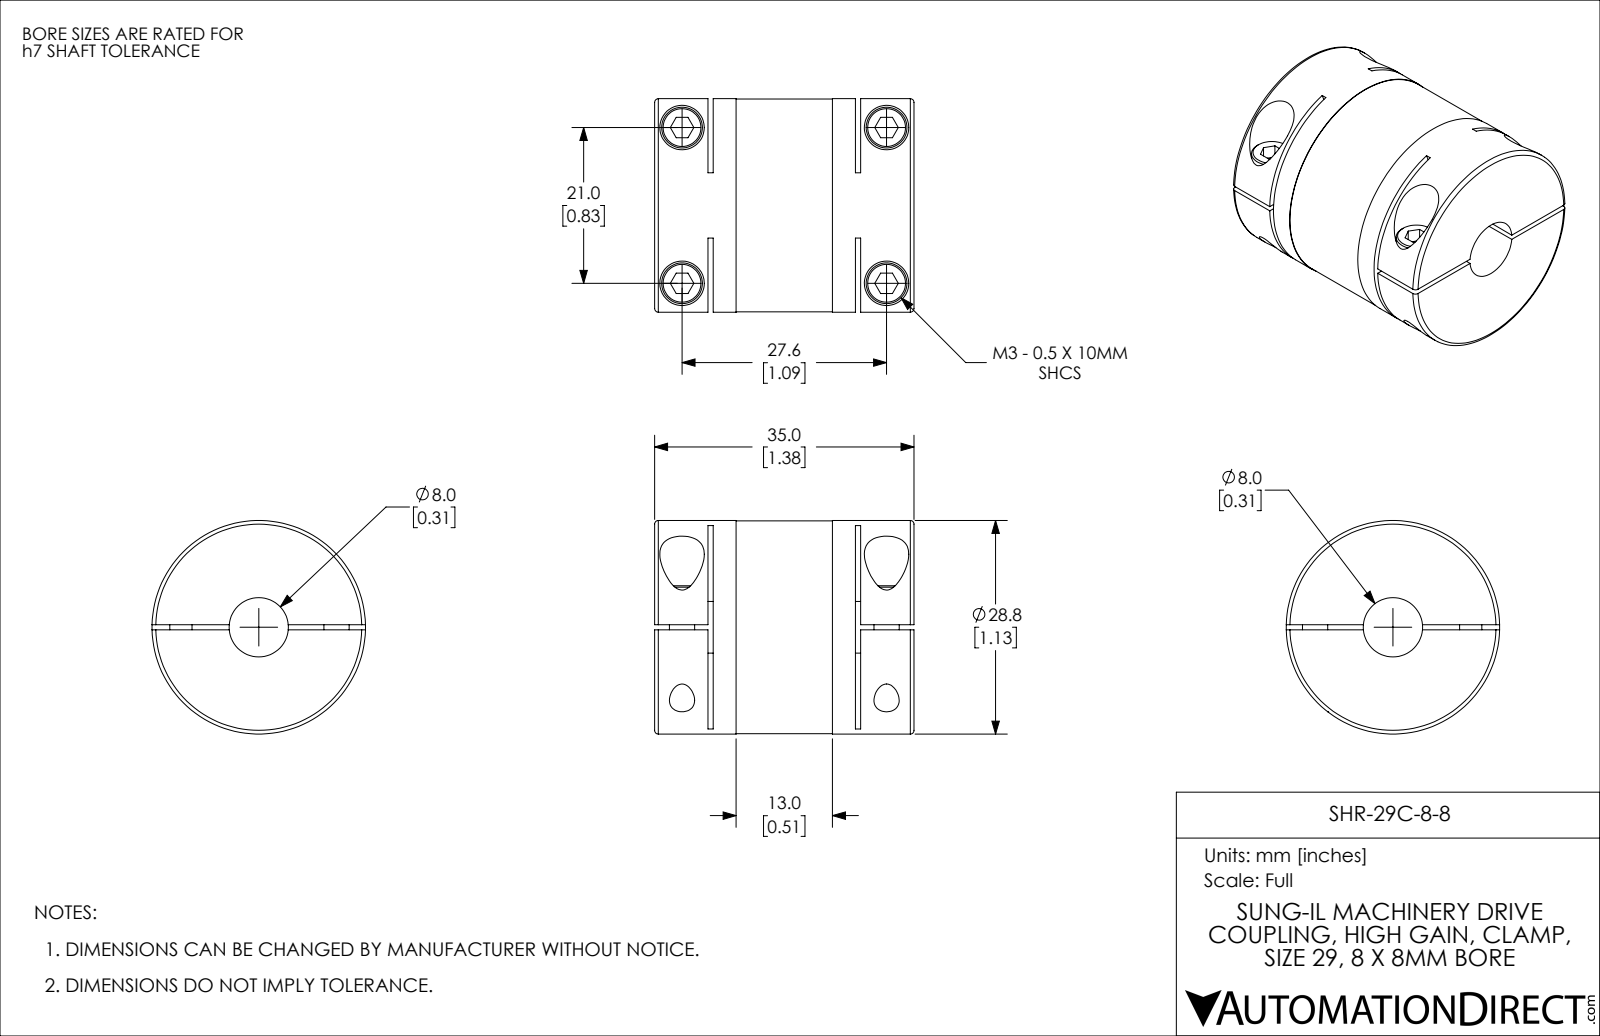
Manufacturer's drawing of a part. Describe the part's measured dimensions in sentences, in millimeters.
The part is named "SHR-29C-8-8". Its 3-D file was written by "SolidWorks 2021 (CONFIG_CONTROL_DESIGN)". It is 1 solid with 145 faces: 70 planar, 57 cylindrical and 18 other. Overall it measures 35 by 28.8 by 28.8 millimeters. Its volume is 19 081 cubic millimeters and its surface area 8 796 square millimeters. Round holes: 4 of diameter 3.4, 4 of diameter 6, 1 of diameter 8, 1 of diameter 10. Round bosses or shafts: 4 of diameter 5.5, 2 of diameter 3, 1 of diameter 28.8, 1 of diameter 28.7. Partial cylindrical surfaces (rounded edges, fillets, slot ends): 2 of radius 37.5. The main face-to-face distances are 0.7, 7.9, 27.1, 7.2, 27.8, 19.9, 35, 19.2, 20.6, 11. The hole center spacings are 21, 27.6, 34.68.
